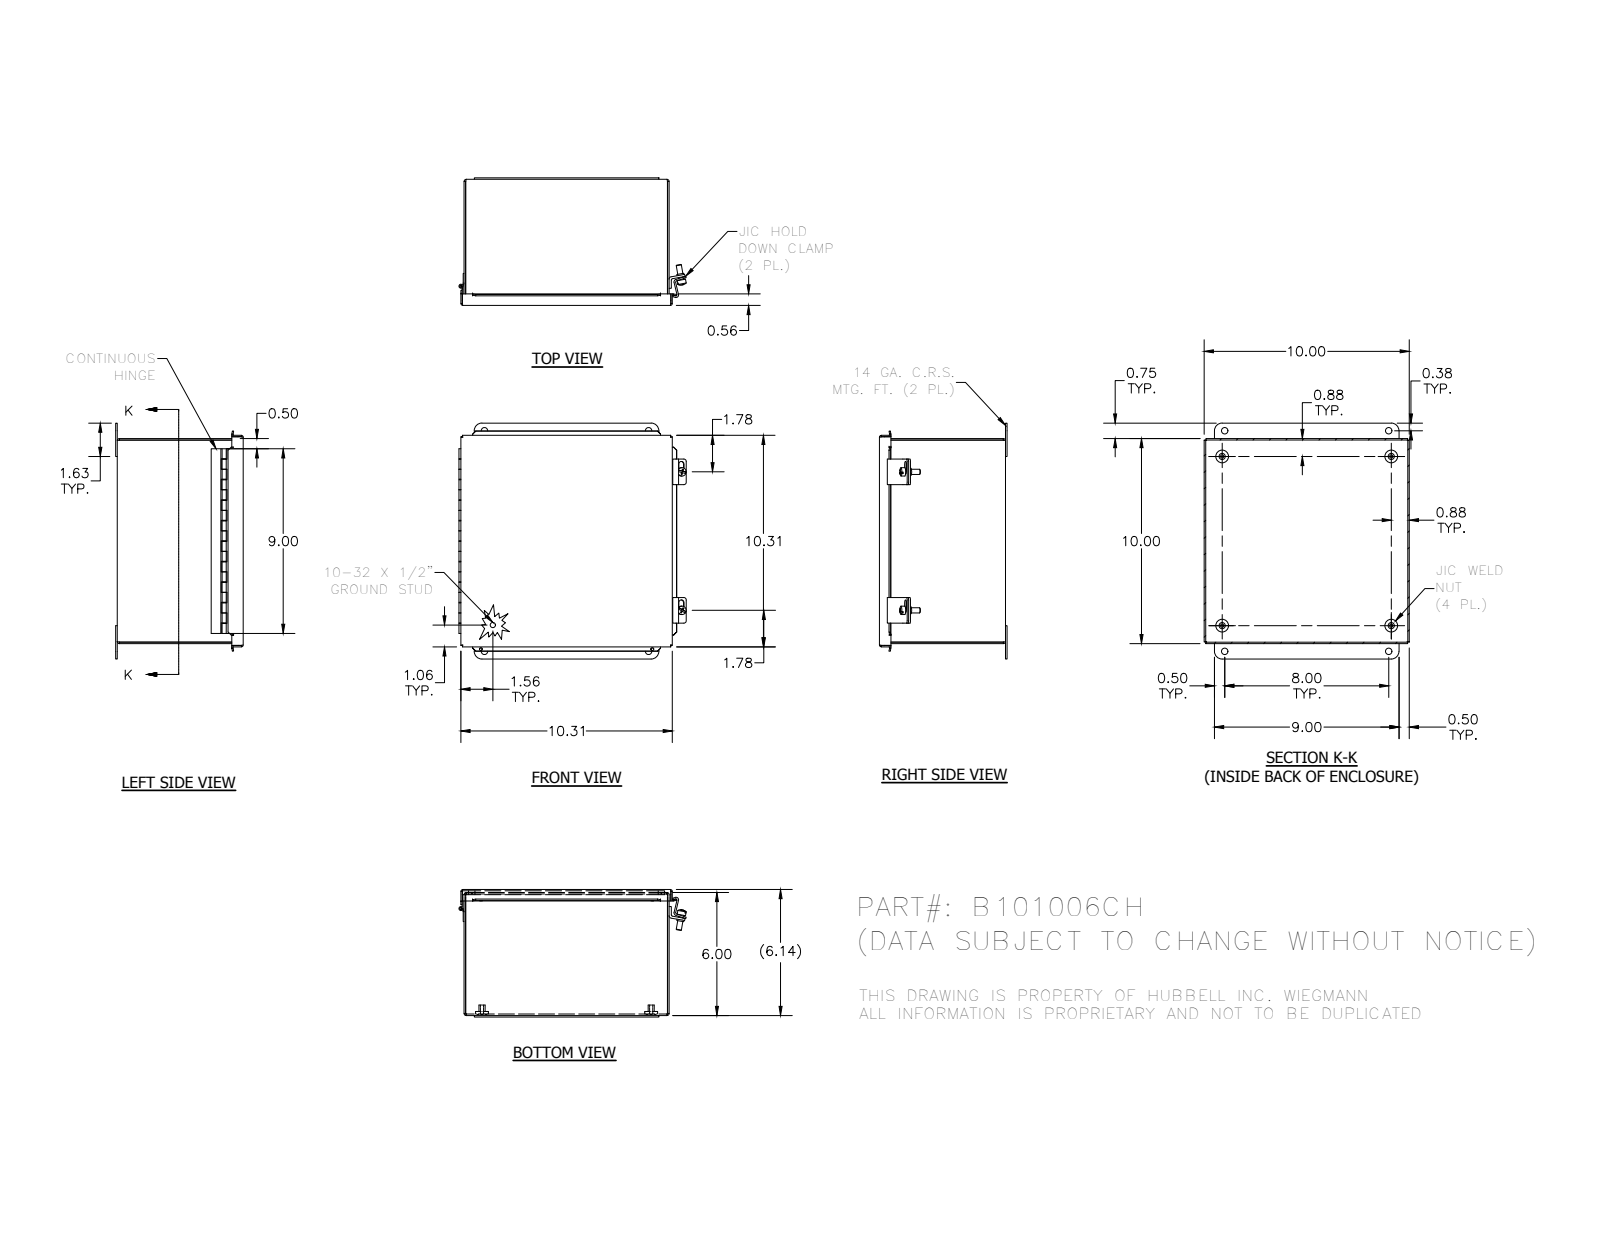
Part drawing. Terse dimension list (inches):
name: B101006CH; 3499; 3484; C1001 (+8 more)
written by: Autodesk Inventor 2012 (AUTOMOTIVE_DESIGN)
unit: in
bodies: 20 solids, 479 faces (311 planar, 123 cylindrical, 45 other)
size: 11.5 × 11.087 × 6.219
volume: 41.86 in³; area: 1 143 in²
holes: 4× ⌀0.156, 4× ⌀0.31, 2× ⌀0.14, 2× ⌀0.196, 1× ⌀0.116
bosses: 4× ⌀0.625, 4× ⌀0.3, 3× ⌀0.25, 2× ⌀0.41, 2× ⌀0.344, 1× ⌀0.2, 1× ⌀0.19, 1× ⌀0.1
rounds: 15× R0.031, 8× R0.105, 8× R0.125, 7× R0.093, 4× R0.133, 4× R0.375, 3× R0.063, 3× R0.126
face distances: 0.074, 9.926, 6.083, 10, 9.852, 0.062, 6.144, 6.009, 6.07, 0.075
hole spacings: 8.221, 8.25, 1.256, 9.501, 12.501, 8, 11.668, 1.256
